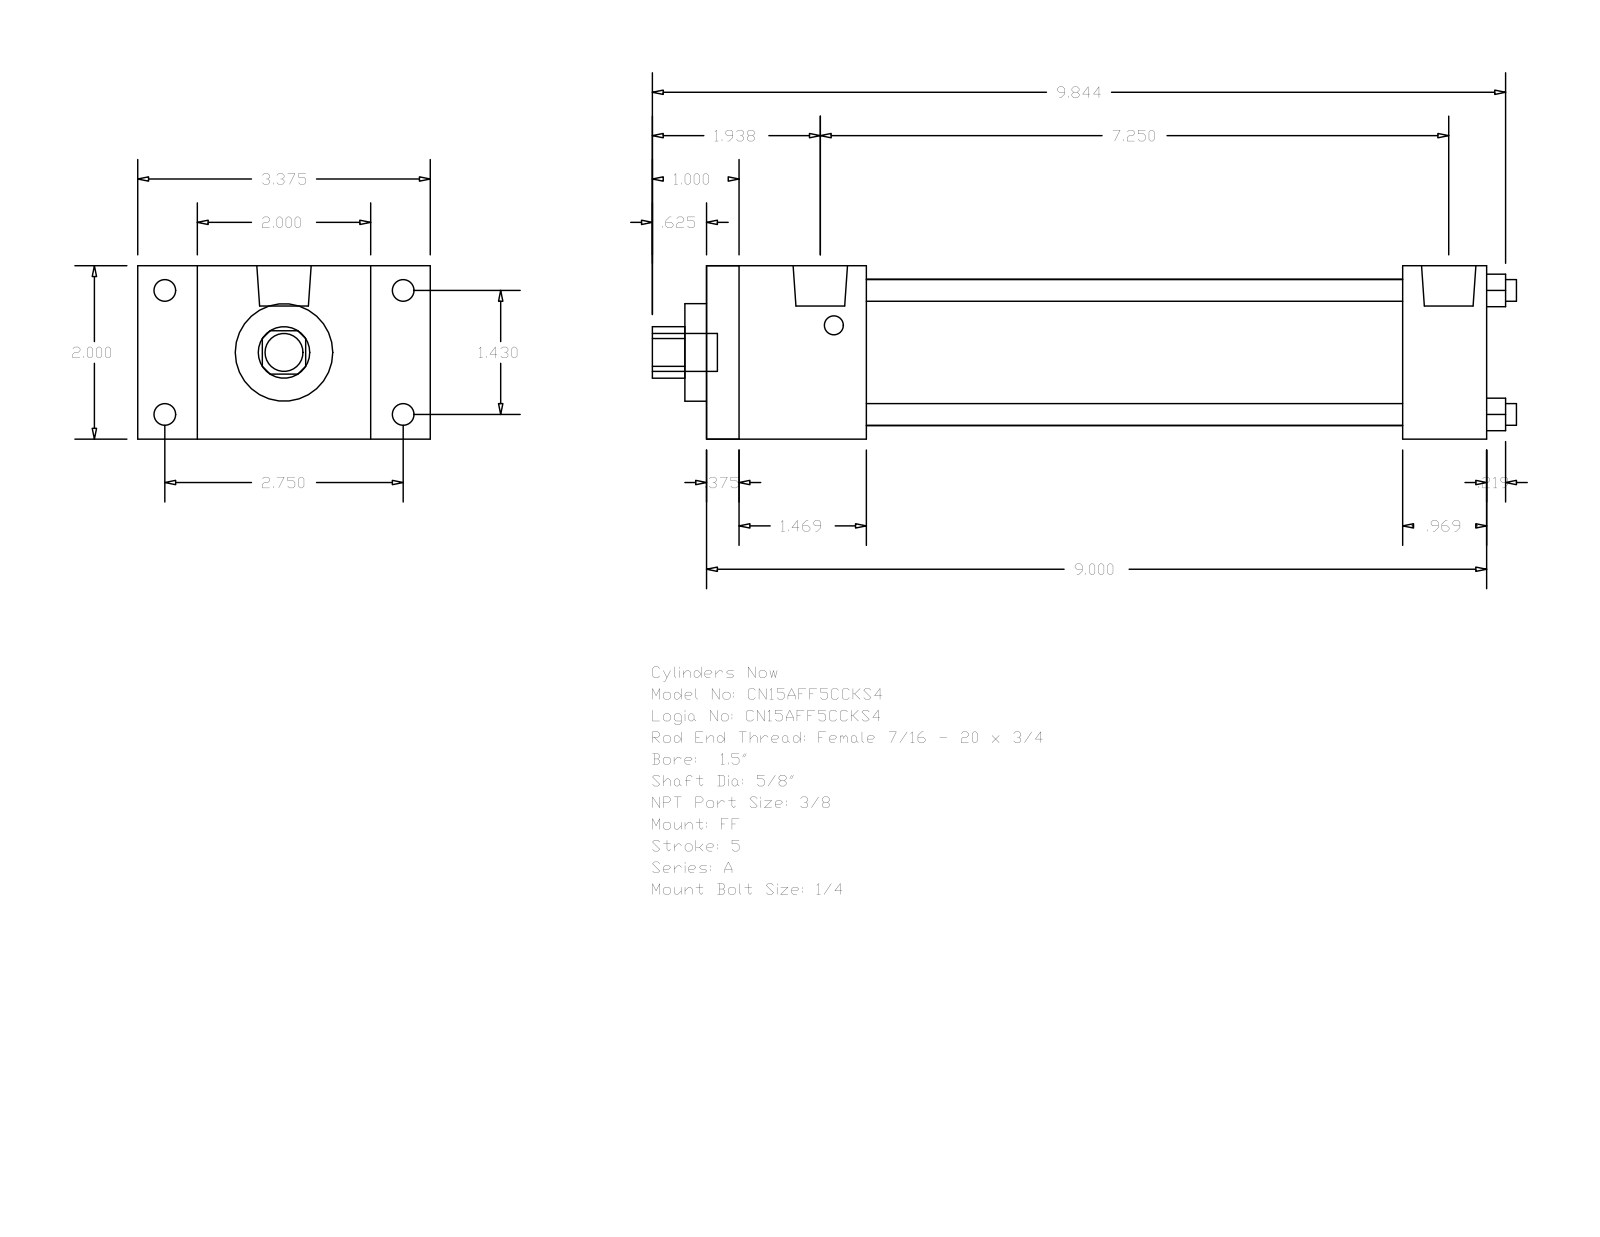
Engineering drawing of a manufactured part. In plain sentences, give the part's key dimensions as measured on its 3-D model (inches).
The part is named "A_FF__0150_0.625". Its 3-D file was written by "GSSL Pune (CONFIG_CONTROL_DESIGN)". It is 0 solids with 92 faces: 64 planar, 28 cylindrical and 0 other. Overall it measures 9.969 by 3.375 by 2 inches. Round holes: 4 of diameter 0.25, 1 of diameter 0.625, 1 of diameter 1.125, 1 of diameter 1.69. Round bosses or shafts: 4 of diameter 0.25, 4 of diameter 0.219, 2 of diameter 0.627, 1 of diameter 0.437. Partial cylindrical surfaces (rounded edges, fillets, slot ends): 1 of radius 0.297. The main face-to-face distances are 2, 9, 0.375, 8.625, 1.844, 8.031, 1.469, 7.656, 6.187, 7.156. The hole center spacings are 1.011, 1.43, 2.022.
